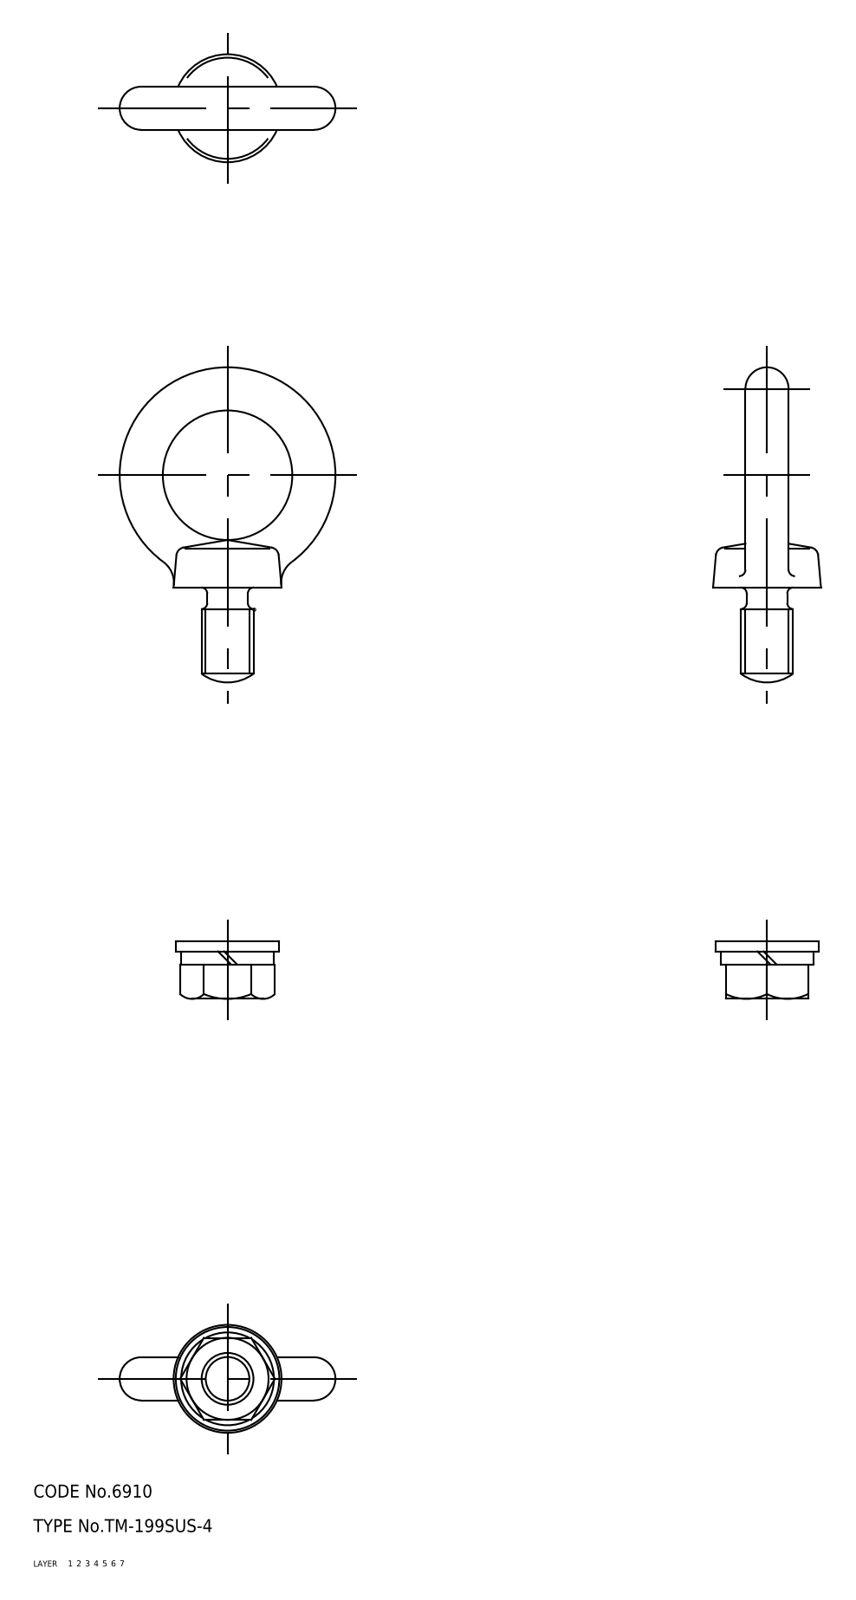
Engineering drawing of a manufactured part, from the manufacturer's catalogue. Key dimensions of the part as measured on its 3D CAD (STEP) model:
Part name (STEP PRODUCT): TM_199SUS_4
STEP written by: SolidWorks 2003240 (AUTOMOTIVE_DESIGN)
Units: millimetres
Bodies: 4 solids, 52 faces (13 planar, 12 cylindrical, 27 other)
Overall size (bounding box): 73 × 50 × 25
Volume: 18 341 mm³ · Surface area: 8 482 mm²
Round holes (diameter × count): ⌀12 ×1
Round bosses / shafts (diameter × count): ⌀24 ×1, ⌀21.5 ×1
Main face-to-face distances: 2.3, 3, 5.3, 19, 8, 11, 13.3
